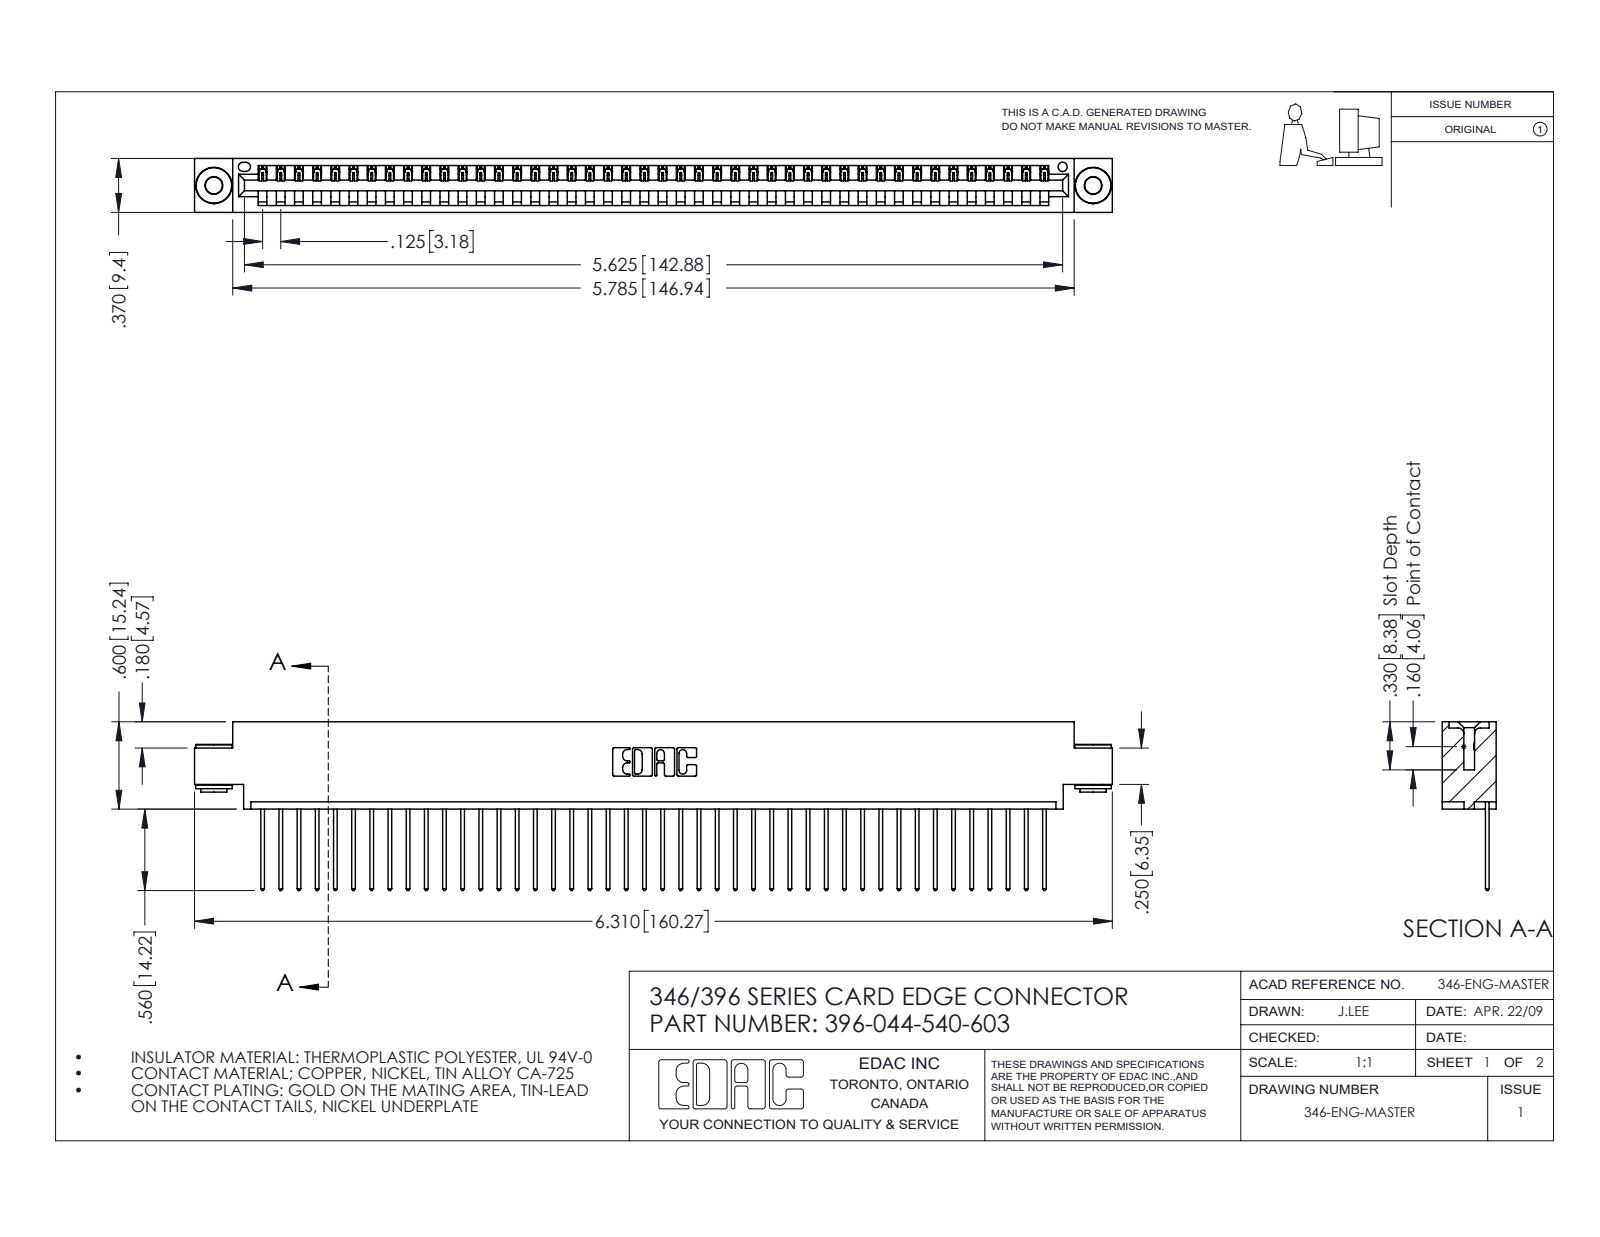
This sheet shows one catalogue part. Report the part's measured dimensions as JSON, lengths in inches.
{"part_name": "396-044-540-603; 345-250-002_345-250-002-102; 345-292-001_345-293-140; 346 Part_0.170 Offset - 0.156 Dia-TH", "step_written_by": "SolidWorks 2016 (CONFIG_CONTROL_DESIGN)", "units": "inches", "bodies": {"solids": 47, "faces": 2716, "planar": 1850, "cylindrical": 858, "other": 8}, "overall_size": [6.31, 1.16, 0.37], "volume_in3": 0.932, "surface_area_in2": 30.9, "round_holes": [[0.116, 2], [0.156, 2], [0.064, 1]], "round_bosses_or_shafts": [[0.25, 2], [0.18, 2], [0.136, 2]], "partial_cylinders_radius": [[0.006, 88], [0.01, 88], [0.01, 22], [0.007, 6], [0.031, 6], [0.026, 3], [0.031, 2], [0.04, 2]], "face_to_face_distances": [0.048, 0.322, 0.37, 0.25, 0.025, 0.072, 0.298, 0.148, 0.222, 0.1], "hole_center_spacings": [0.246, 5.836, 6.045]}
